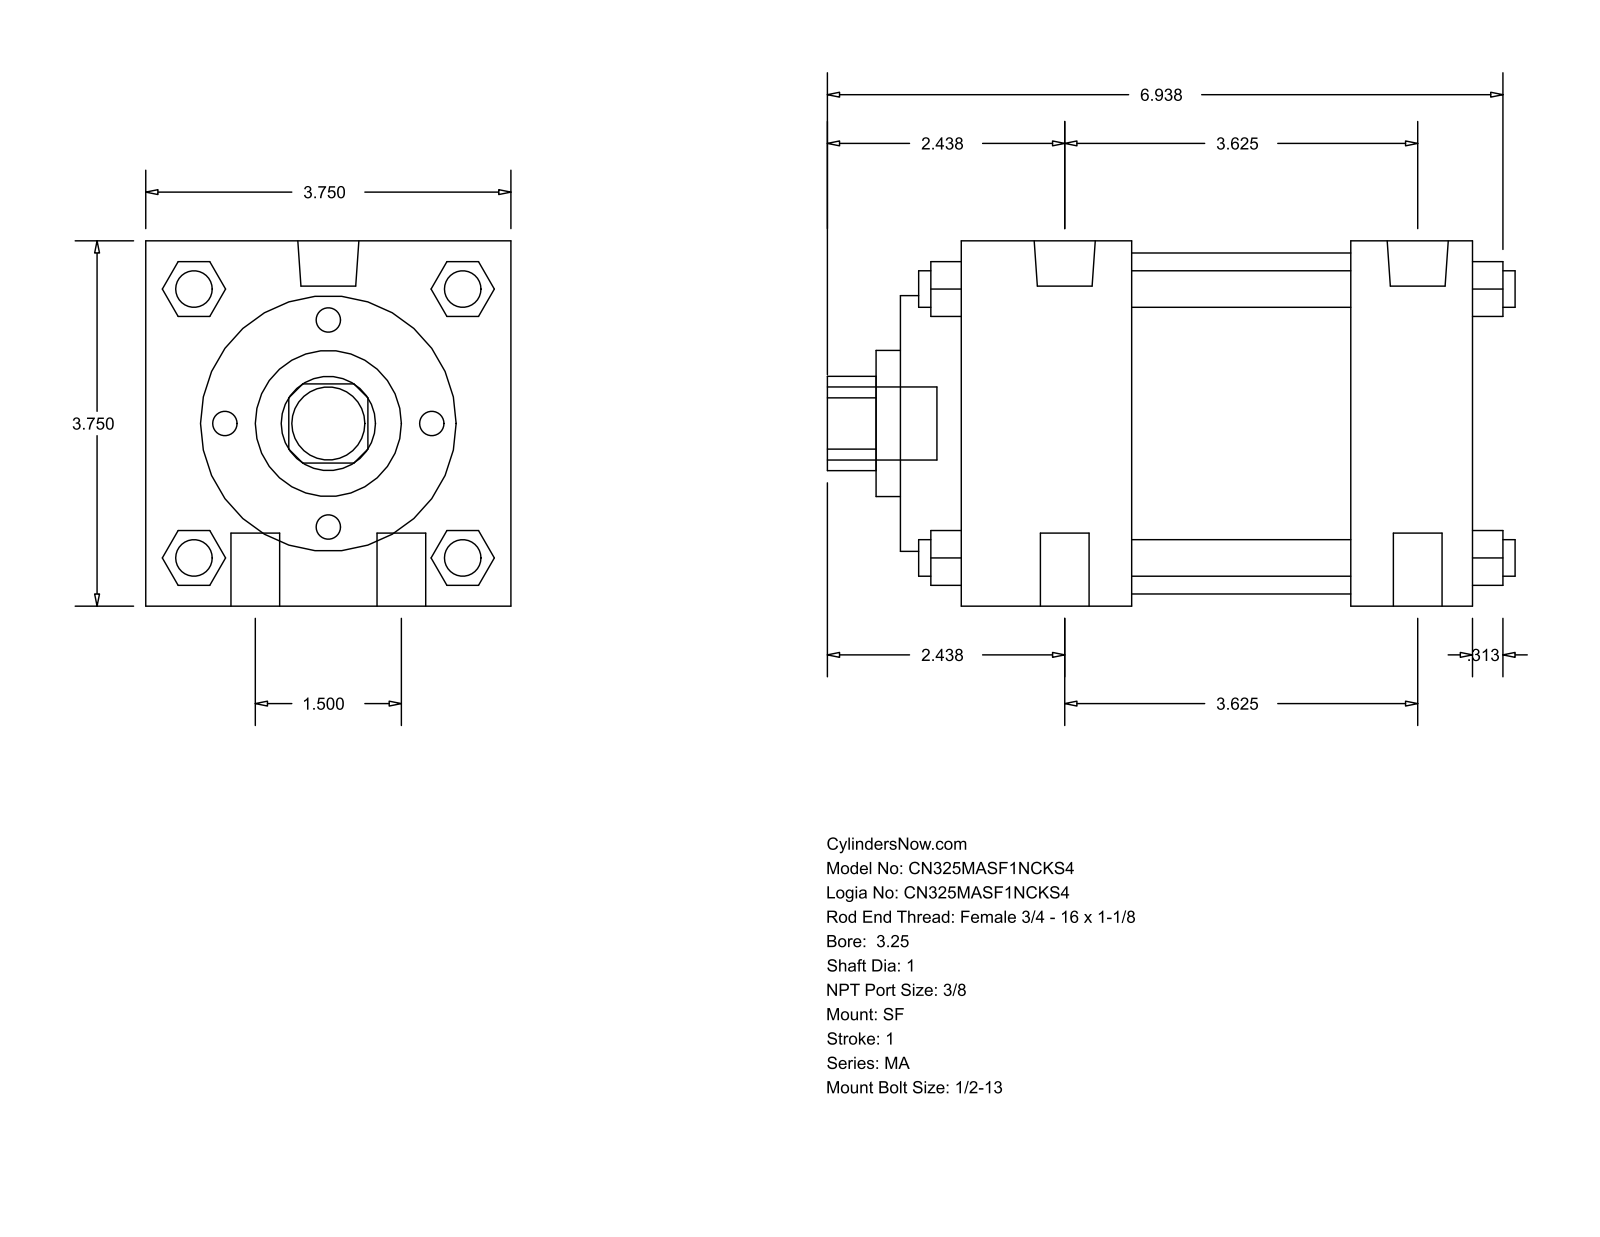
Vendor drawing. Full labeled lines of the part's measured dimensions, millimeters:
Part name (STEP PRODUCT): MA_SF__0325_1
STEP written by: GSSL Pune (CONFIG_CONTROL_DESIGN)
Units: millimetres
Bodies: 0 solids, 126 faces (95 planar, 31 cylindrical, 0 other)
Overall size (bounding box): 179.39 × 95.25 × 95.25
Round holes (diameter × count): ⌀25.4 ×1, ⌀38.1 ×1, ⌀66.67 ×1, ⌀88.9 ×1
Round bosses / shafts (diameter × count): ⌀12.7 ×4, ⌀9.53 ×4, ⌀15.93 ×2, ⌀11.11 ×2, ⌀19.05 ×1
Partial cylindrical surfaces — rounded edges, fillets, slot ends (radius × count): R12.29 ×1
Main face-to-face distances: 95.24, 133.36, 15.87, 101.61, 31.75, 44.46, 57.15, 88.9, 60.33, 117.48
